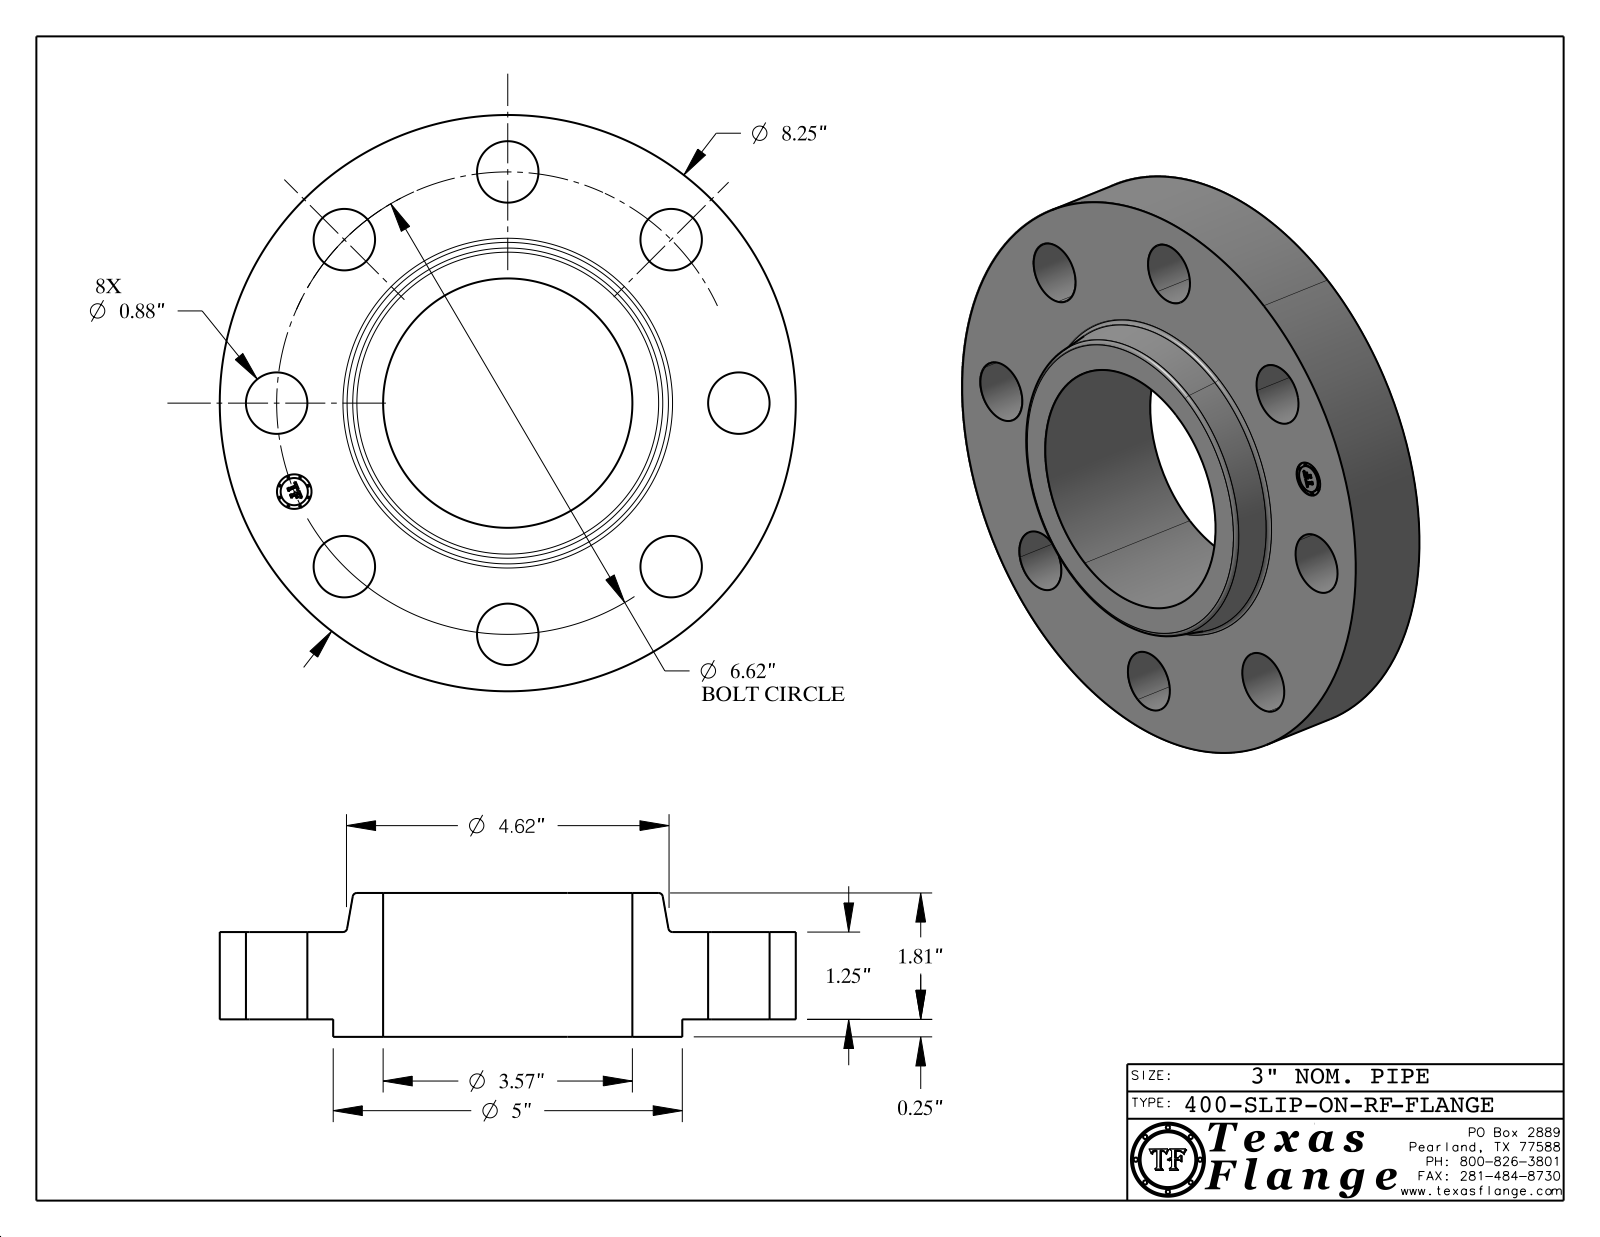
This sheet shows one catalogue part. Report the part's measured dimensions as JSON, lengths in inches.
{"part_name": "400-SLIP-ON-RF", "step_written_by": "CATIA V5 STEP AP214 (AUTOMOTIVE_DESIGN)", "units": "inches", "bodies": {"solids": 1, "faces": 417, "planar": 369, "cylindrical": 42, "other": 6}, "overall_size": [8.25, 8.25, 2.06], "volume_in3": 54.02, "surface_area_in2": 170.5, "round_holes": [[0.88, 8], [0.495, 1], [3.57, 1]], "round_bosses_or_shafts": [[0.03, 8], [8.25, 1], [5, 1], [0.39, 1]], "face_to_face_distances": [1.25, 0.25, 1.5, 2.06, 1.81, 0.56, 0.015, 1.485, 1.235, 0.575], "hole_center_spacings": [3.31, 2.533, 6.116, 4.681, 4.681, 1.291, 3.678, 6.493]}
